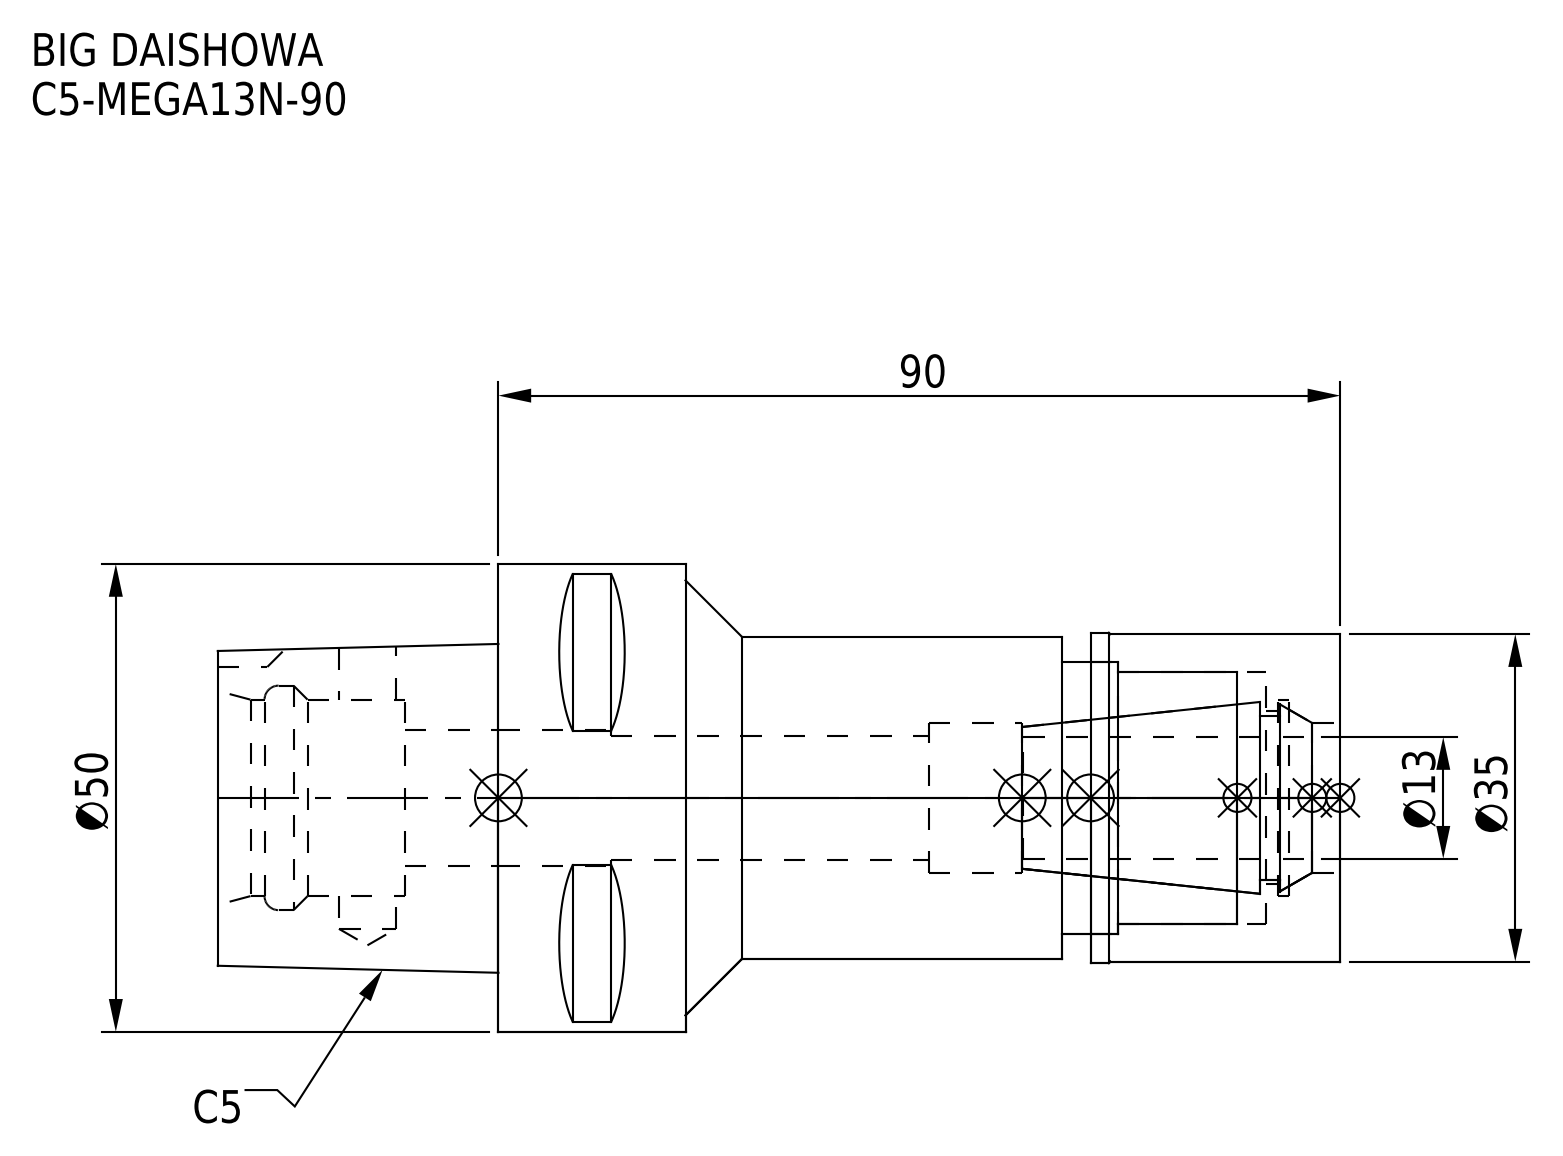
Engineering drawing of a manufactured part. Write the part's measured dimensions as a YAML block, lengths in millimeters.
part_name: "C5-MEGA13N-90_1.stp; MGN13_1.stp; C5-MEGA13N-90-130.stp; C5-MEGA13N-90 (+3 more)"
step_written_by: "SolidWorks 2019 (CONFIG_CONTROL_DESIGN)"
units: millimeters
bodies: {solids: 2, faces: 95, planar: 38, cylindrical: 39, other: 18}
overall_size: [120, 50, 50]
volume: 105981
surface_area: 28085
round_holes:
  - {diameter: 6.1, count: 1}
  - {diameter: 13.3, count: 1}
  - {diameter: 14.5, count: 1}
  - {diameter: 16, count: 1}
  - {diameter: 18.5, count: 1}
  - {diameter: 21, count: 1}
  - {diameter: 24, count: 1}
  - {diameter: 27, count: 1}
  - {diameter: 29, count: 1}
round_bosses_or_shafts:
  - {diameter: 50, count: 1}
  - {diameter: 35.3, count: 1}
  - {diameter: 35, count: 1}
  - {diameter: 34.5, count: 1}
partial_cylinders:
  - {radius: 4, count: 1}
face_to_face_distances: [90, 30, 20, 63.3, 93.3, 120, 8, 26.7, 18.7, 82]
